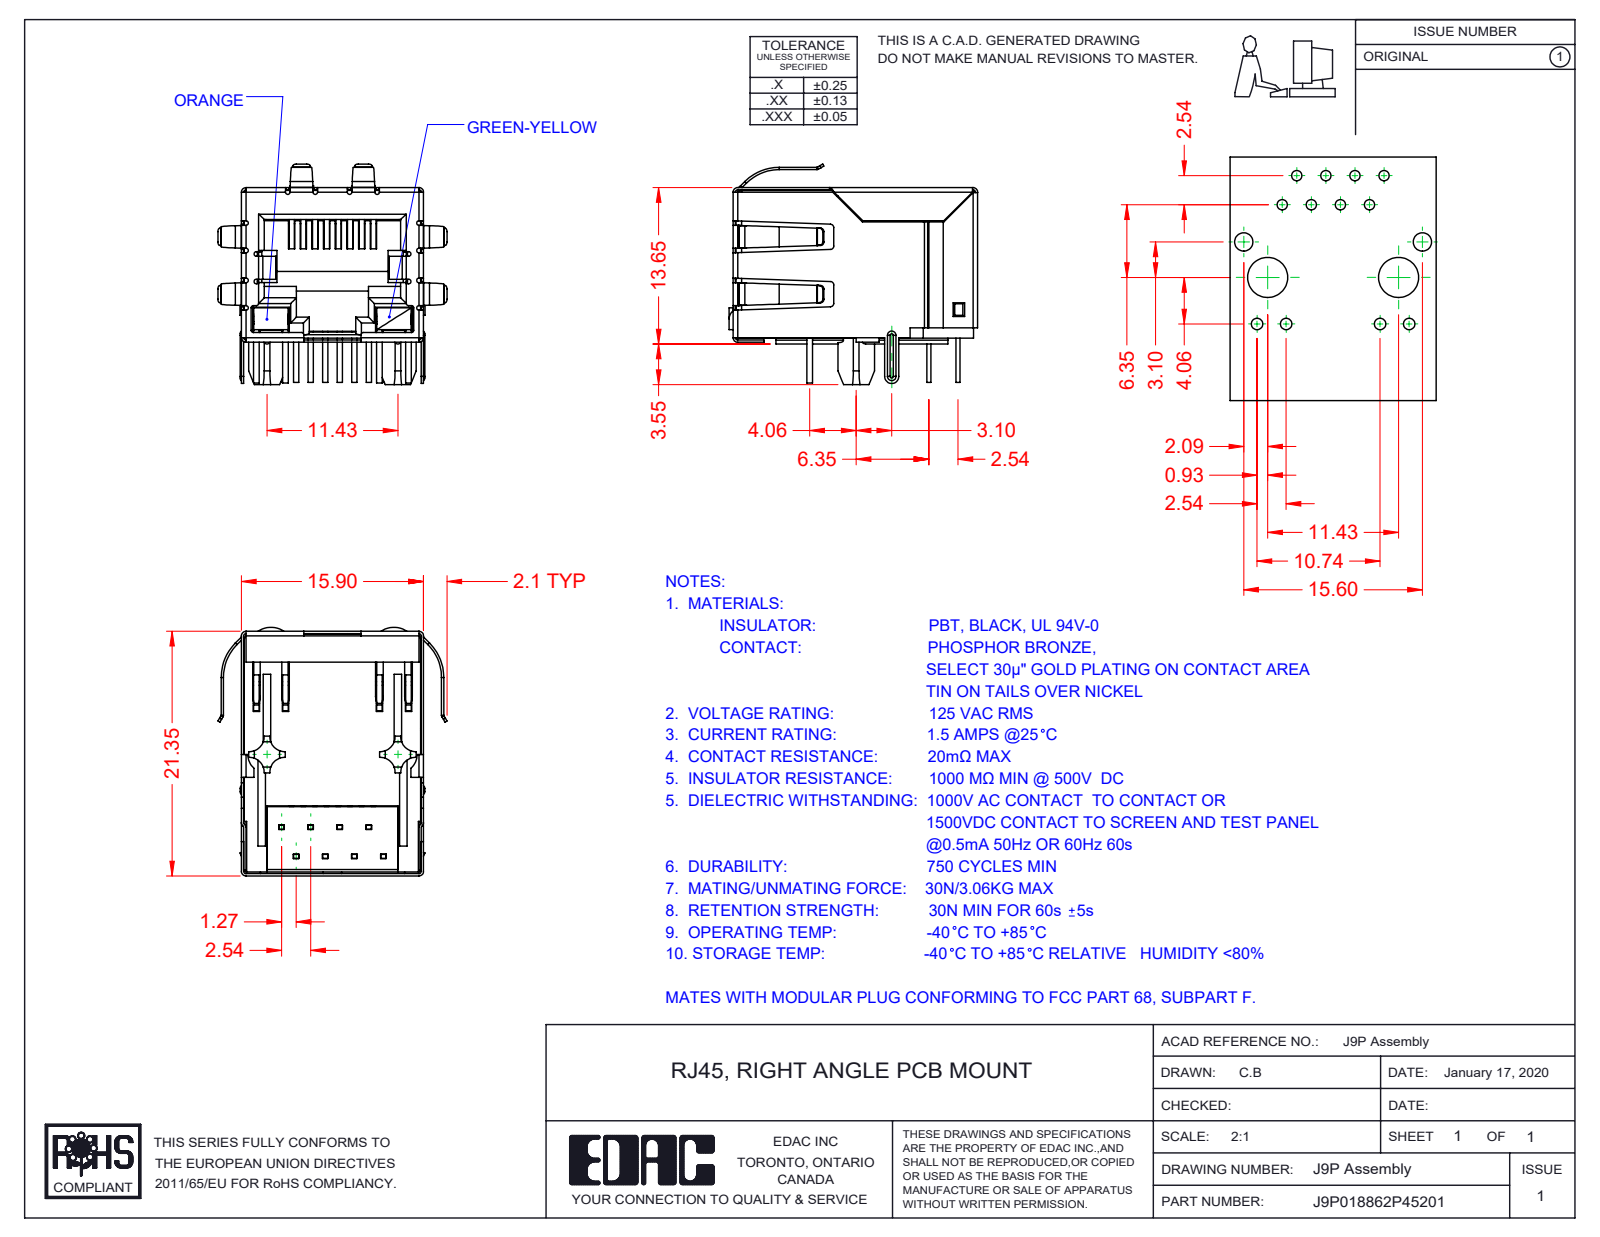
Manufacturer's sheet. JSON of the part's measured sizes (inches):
{"part_name": "9P-LED Insulator; 9P-LED Contacts; 9P-LED LED RH_5-Green-Yellow; 9P-LED Contact Lock (+4 more)", "step_written_by": "SolidWorks 2016 (CONFIG_CONTROL_DESIGN)", "units": "inches", "bodies": {"solids": 13, "faces": 1474, "planar": 1042, "cylindrical": 338, "other": 94}, "overall_size": [0.854, 0.787, 0.758], "volume_in3": 0.164, "surface_area_in2": 11.65, "partial_cylinders_radius": [[0.008, 39], [0.02, 22], [0.012, 20], [0.016, 16], [0.051, 8], [0.009, 5], [0.004, 4], [0.012, 4]], "face_to_face_distances": [0.608, 0.618, 0.616, 0.014, 0.021, 0.61, 0.487, 0.024, 0.055, 0.023]}
